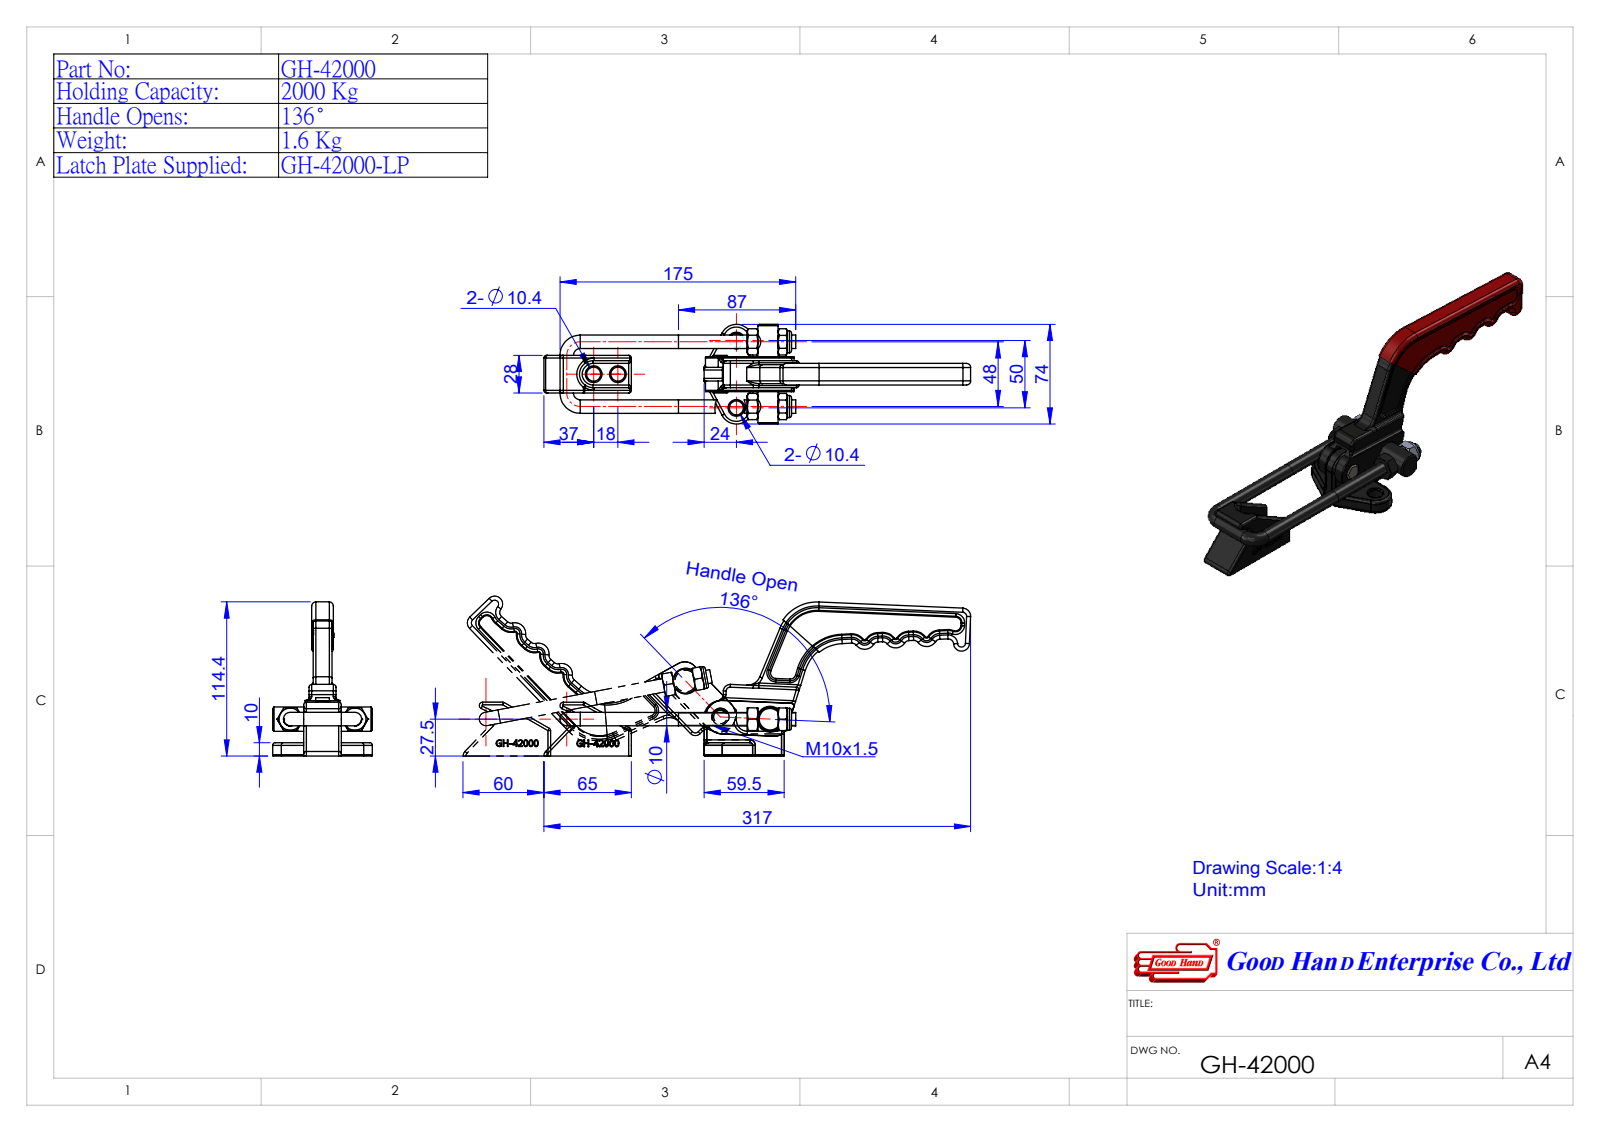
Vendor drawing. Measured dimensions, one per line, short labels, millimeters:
name: 止付螺絲M5x6尖尾-1^GH-42000(簡化); GH-42000(簡化); Group1^GH-42000(簡化); 24200014-1^GH-42000(簡化) (+3 more)
written by: SolidWorks 2016 (AUTOMOTIVE_DESIGN)
unit: mm
bodies: 9 solids, 485 faces (124 planar, 163 cylindrical, 198 other)
size: 316.9 × 115.44 × 74
volume: 218 615 mm³; area: 69 629 mm²
holes: 4× ⌀10.4, 3× ⌀10, 2× ⌀10.5, 2× ⌀11.45, 1× ⌀4.2, 1× ⌀18
bosses: 3× ⌀10, 2× ⌀16.3, 1× ⌀5
rounds: 31× R2, 14× R3, 13× R4, 6× R1, 4× R8, 3× R5, 3× R10, 3× R12
face distances: 1, 7, 20, 21, 1.9, 12.1, 3, 8.9, 19.1, 6
hole spacings: 48, 91.48, 108.91, 18, 37, 50
